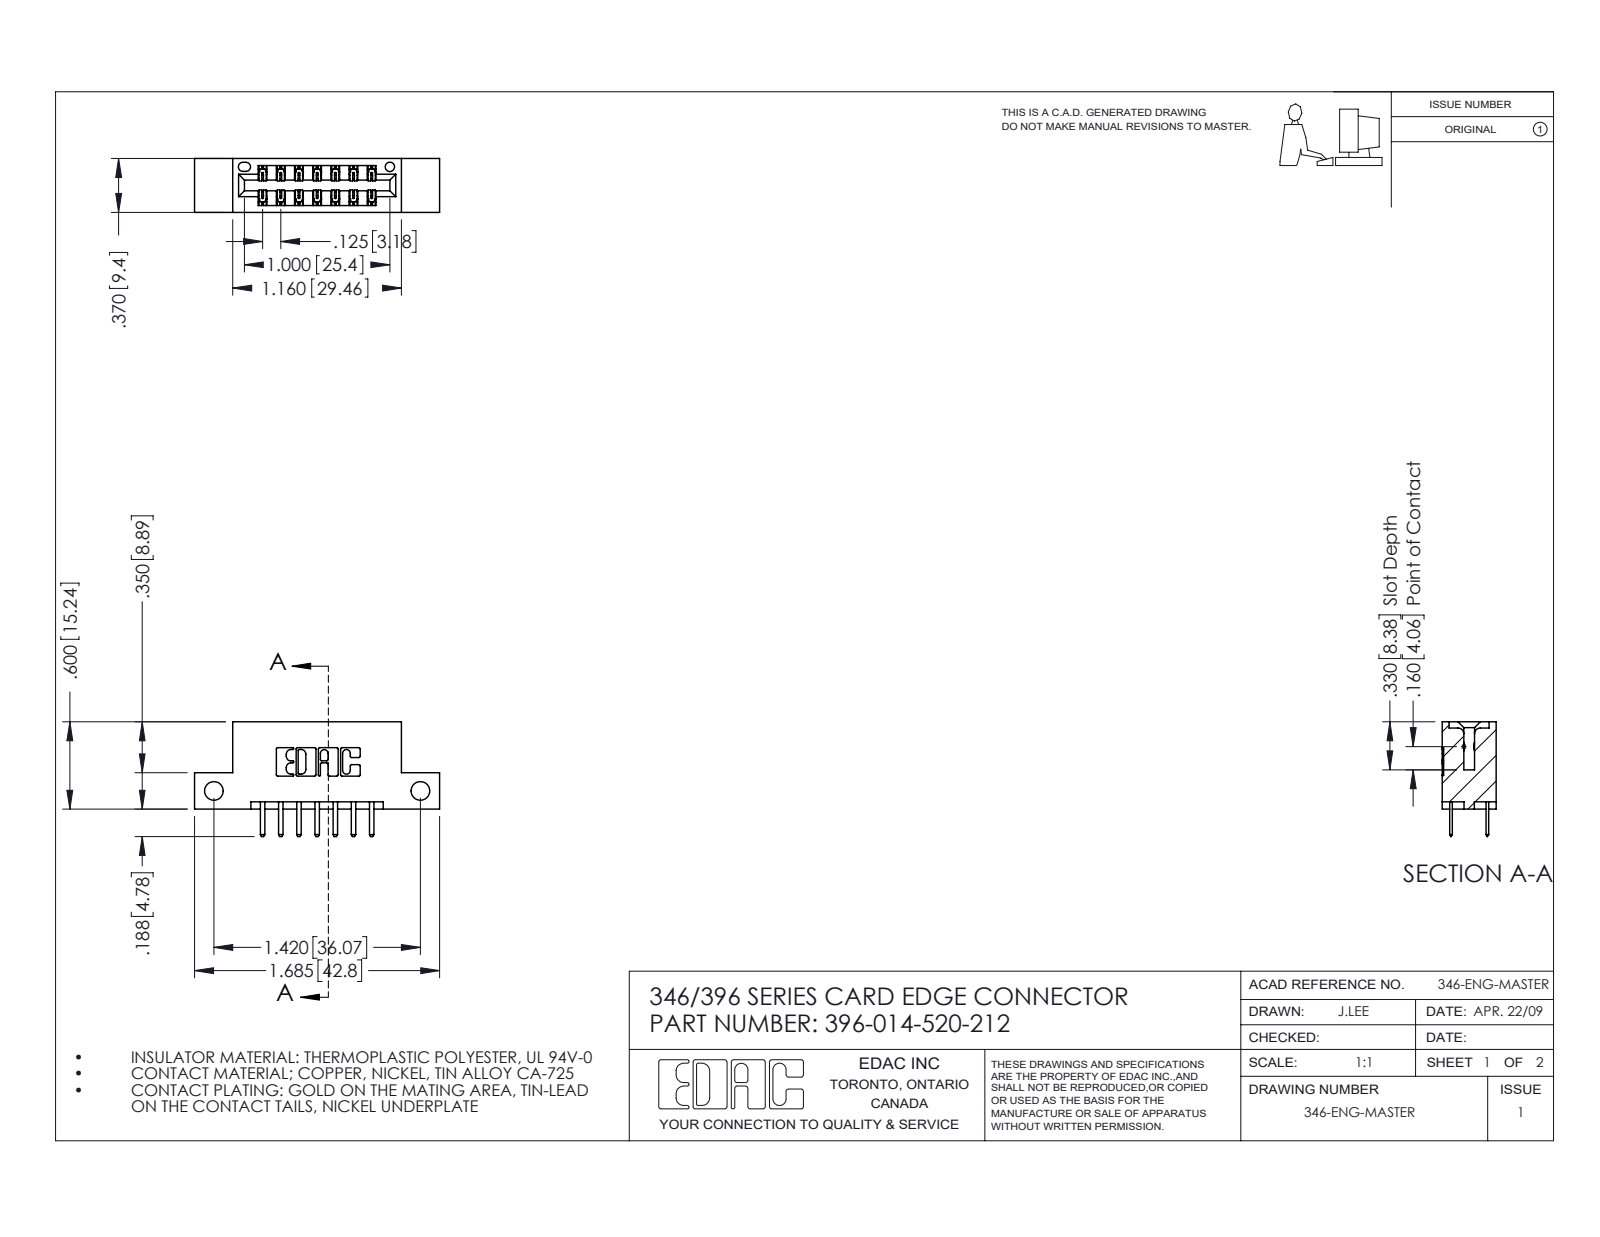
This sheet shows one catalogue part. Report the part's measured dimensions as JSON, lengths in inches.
{"part_name": "345-292-001_345-293-120; 346 Part_Flush Mounting Lugs - Side Mount; 396-014-520-212", "step_written_by": "SolidWorks 2016 (CONFIG_CONTROL_DESIGN)", "units": "inches", "bodies": {"solids": 15, "faces": 906, "planar": 594, "cylindrical": 312, "other": 0}, "overall_size": [1.685, 0.788, 0.37], "volume_in3": 0.232, "surface_area_in2": 7.026, "round_holes": [[0.128, 2], [0.064, 1]], "partial_cylinders_radius": [[0.01, 22], [0.006, 21], [0.01, 18], [0.007, 6], [0.031, 6], [0.026, 3], [0.014, 2], [0.022, 2]], "face_to_face_distances": [0.25, 0.37, 0.048, 0.322, 0.148, 0.222, 0.1, 0.174, 0.125, 0.185], "hole_center_spacings": [1.42]}
